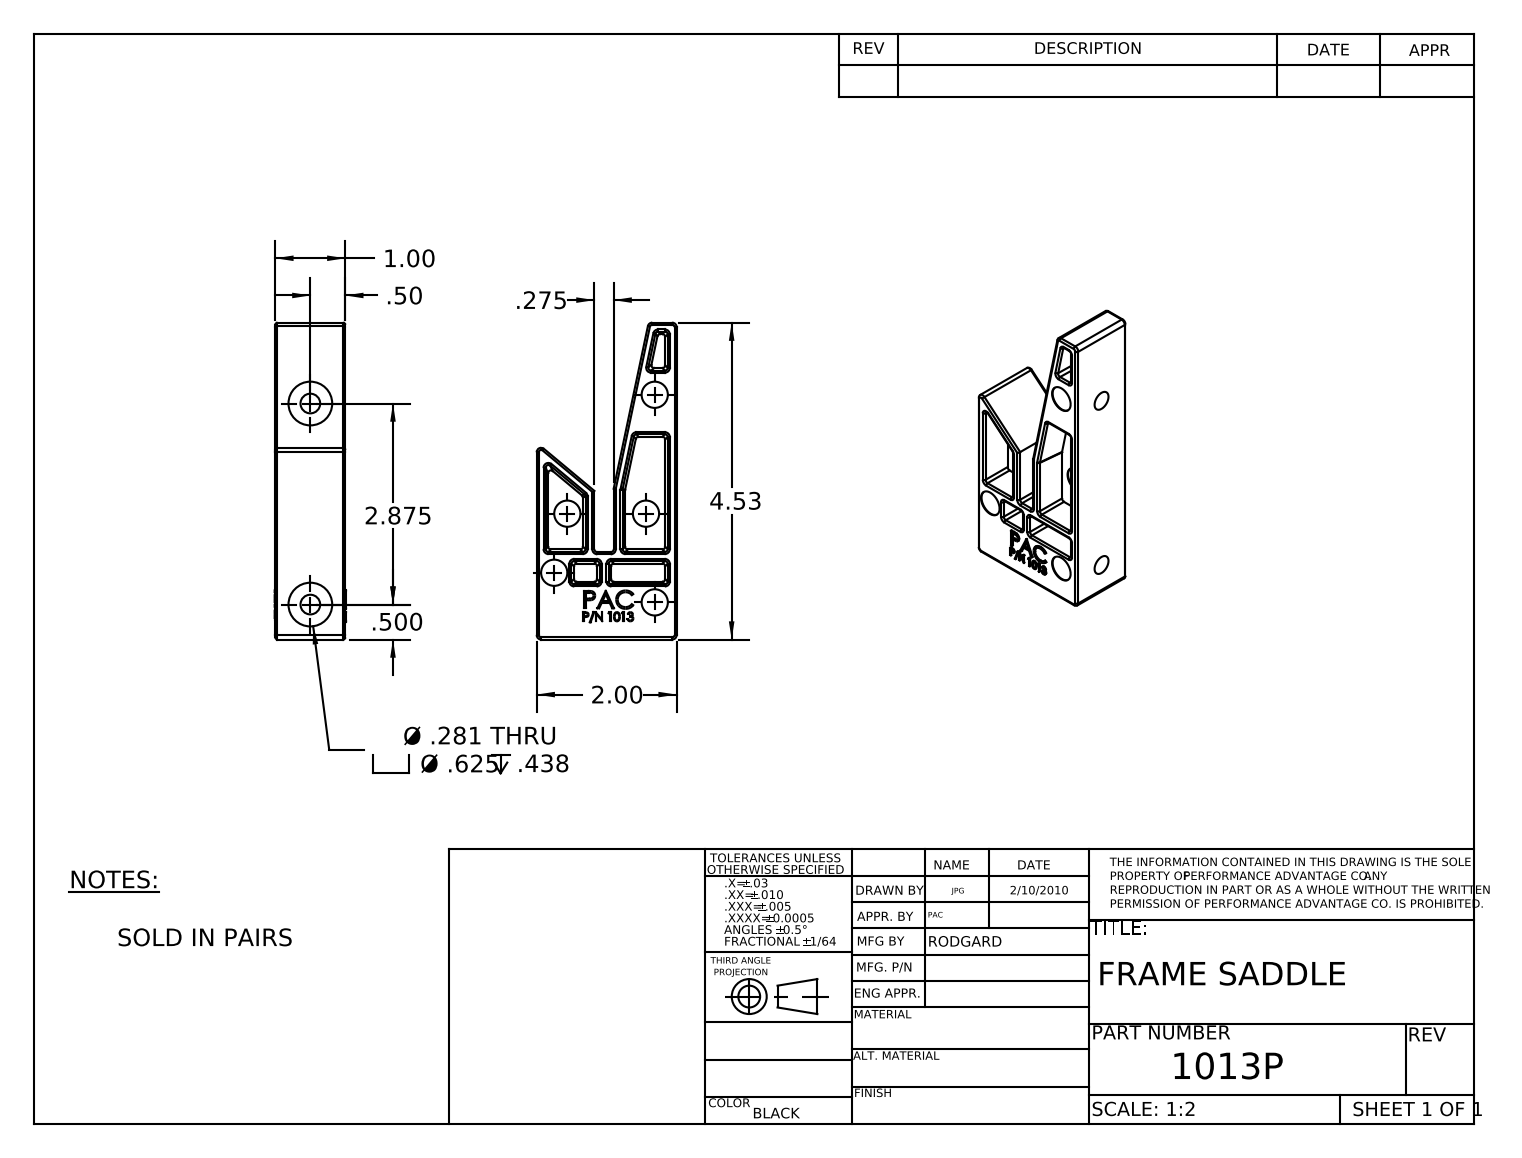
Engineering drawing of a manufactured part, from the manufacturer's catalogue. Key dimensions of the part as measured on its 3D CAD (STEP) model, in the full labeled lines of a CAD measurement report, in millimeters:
Part name (STEP PRODUCT): 1013
STEP written by: SolidWorks 2010 (CONFIG_CONTROL_DESIGN)
Units: millimetres
Bodies: 1 solid, 140 faces (85 planar, 11 cylindrical, 44 other)
Overall size (bounding box): 115.1 × 50.8 × 25.4
Volume: 90 280 mm³ · Surface area: 19 210 mm²
Round holes (diameter × count): ⌀7.1 ×2, ⌀15.9 ×2
Partial cylindrical surfaces — rounded edges, fillets, slot ends (radius × count): R2.4 ×3
Main face-to-face distances: 25.4, 50.8, 27.9, 22.9, 6.7, 21.2, 29.6, 115.1, 45.7, 24.5
Hole centre spacings: 73
